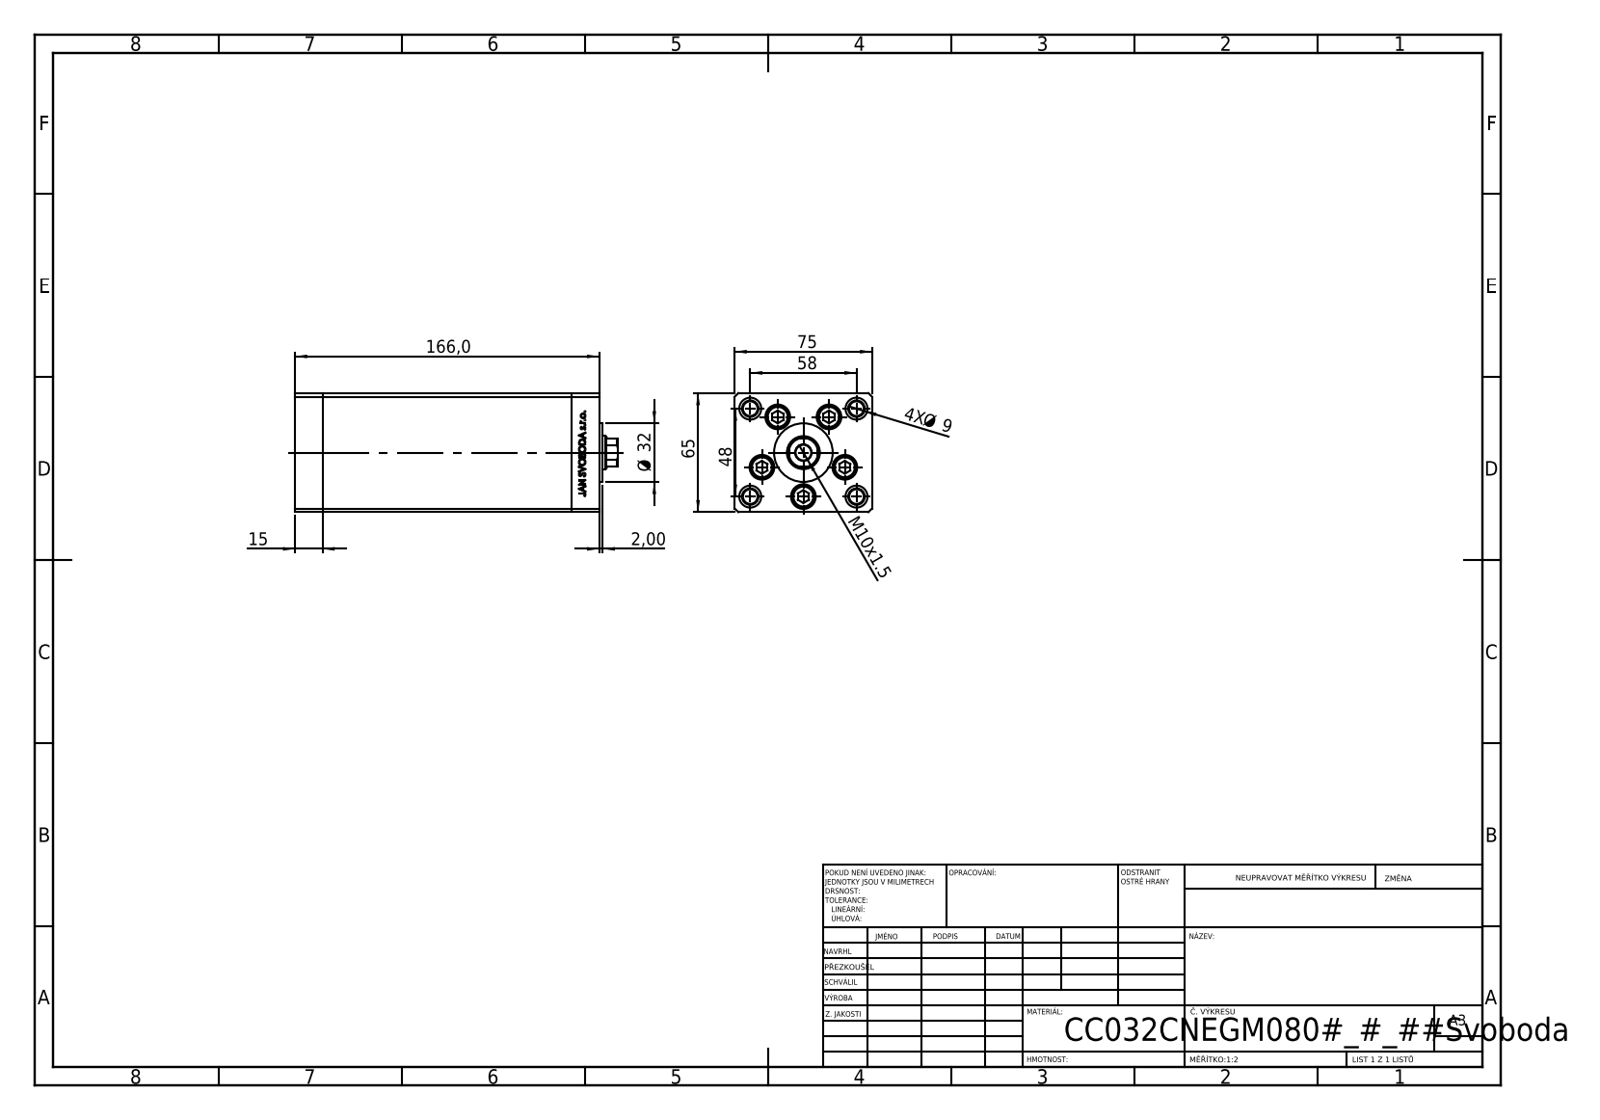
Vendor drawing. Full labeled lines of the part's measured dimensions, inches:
Part name (STEP PRODUCT): V220C_VC_C; V220C BACK_C; ALLEN BOLT; V220C FRONT (+1 more)
STEP written by: SolidWorks 2019 (CONFIG_CONTROL_DESIGN)
Units: inches
Bodies: 13 solids, 1159 faces (538 planar, 159 cylindrical, 462 other)
Overall size (bounding box): 6.929 × 2.953 × 2.559
Volume: 41.75 in³ · Surface area: 219 in²
Round holes (diameter × count): ⌀0.354 ×9, ⌀0.531 ×5, ⌀0.315 ×4, ⌀0.472 ×4, ⌀0.335 ×1, ⌀0.492 ×1, ⌀0.709 ×1
Round bosses / shafts (diameter × count): ⌀0.315 ×5, ⌀0.492 ×4, ⌀1.26 ×1
Partial cylindrical surfaces — rounded edges, fillets, slot ends (radius × count): R0.037 ×2, R0.335 ×1
Main face-to-face distances: 2.953, 2.559, 0.591, 5.354, 5.945, 6.535, 1.102, 5.591, 0.354, 2.146
Hole centre spacings: 0.945, 1.482, 0.617, 0.678, 1.091, 1.135, 1.142, 1.285
